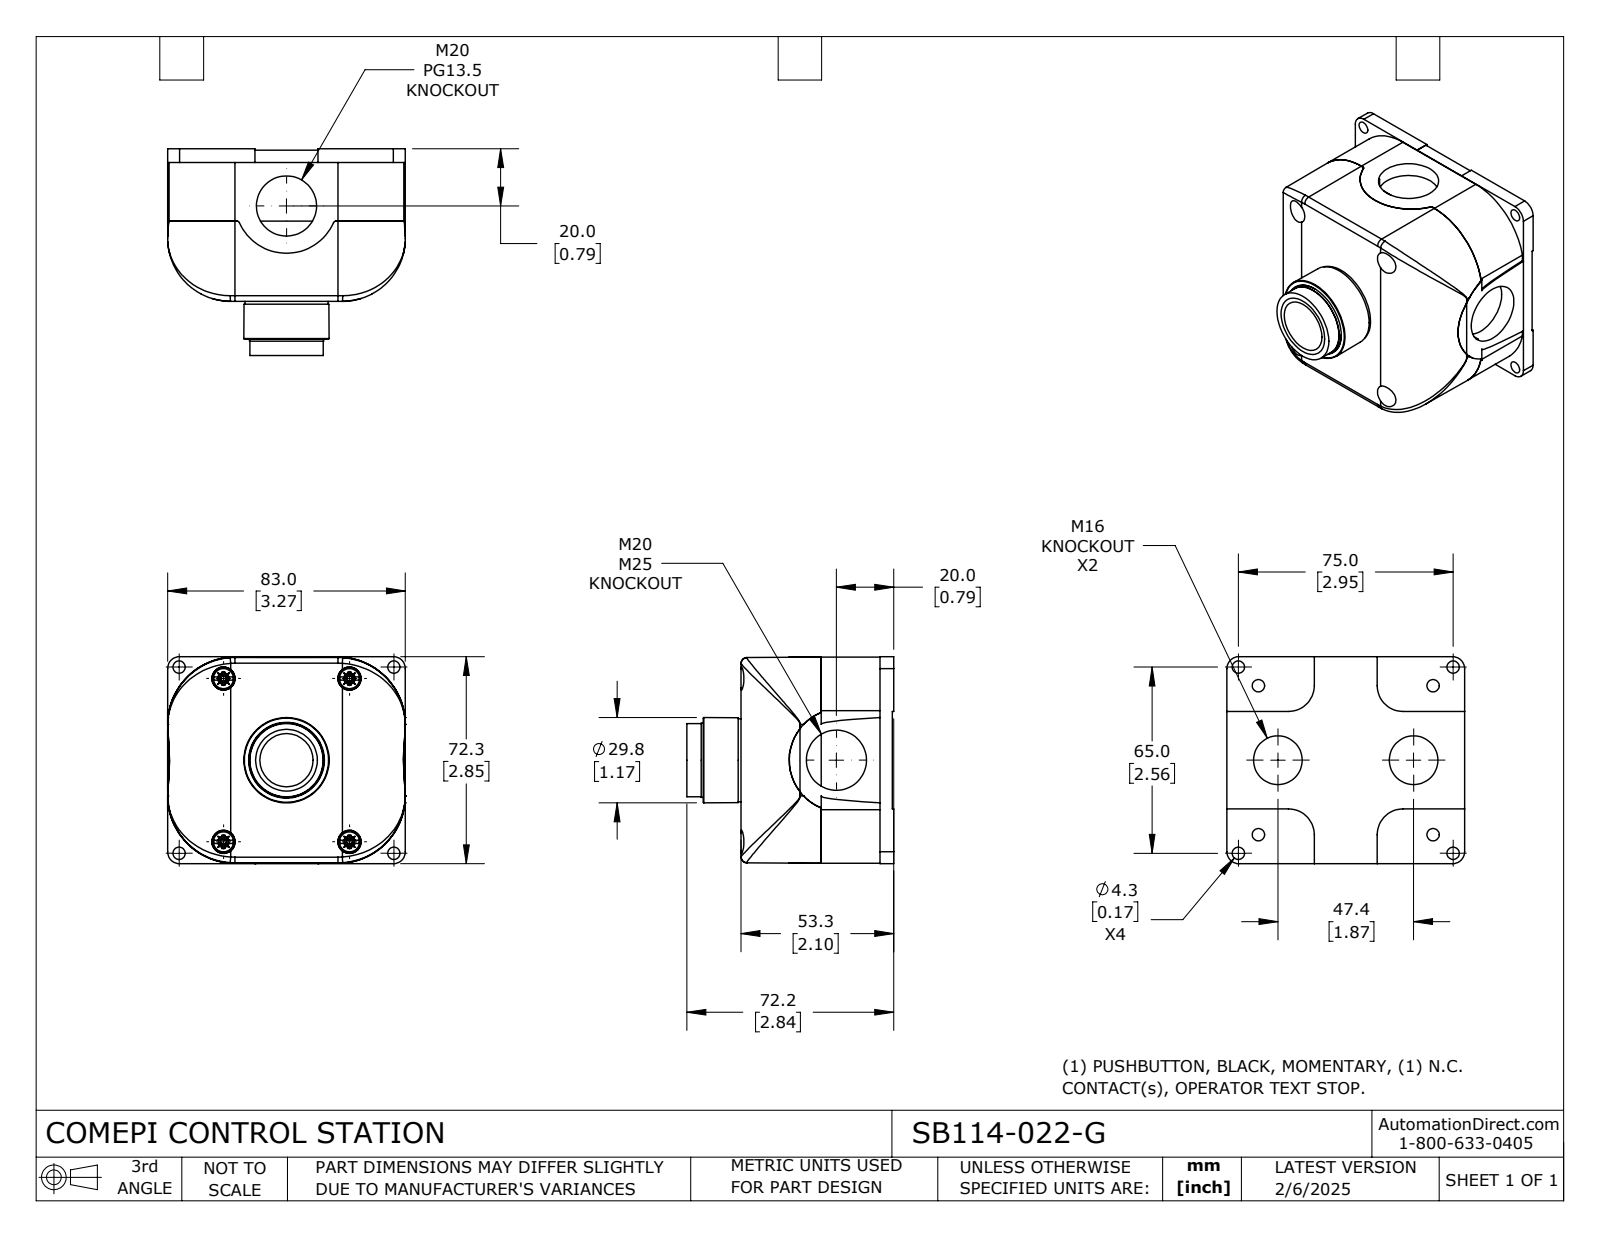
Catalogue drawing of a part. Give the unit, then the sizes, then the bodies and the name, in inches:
Units: inches
Overall size (bounding box): 3.268 × 2.846 × 2.843
Round holes (diameter × count): ⌀0.169 ×8, ⌀0.323 ×4, ⌀0.669 ×2, ⌀0.827 ×2, ⌀0.531 ×1, ⌀0.713 ×1, ⌀0.854 ×1
Round bosses / shafts (diameter × count): ⌀0.276 ×4, ⌀1.142 ×1, ⌀1.02 ×1, ⌀1.008 ×1, ⌀0.748 ×1, ⌀0.728 ×1, ⌀0.63 ×1, ⌀0.614 ×1
Partial cylindrical surfaces — rounded edges, fillets, slot ends (radius × count): R0.035 ×4, R0.079 ×4, R0.354 ×4, R0.38 ×4, R0.925 ×4, R0.008 ×2, R0.01 ×2, R0.709 ×2
Main face-to-face distances: 0.976, 0.098, 0.878, 2.079, 1.98, 1.102, 0.118, 2.098, 0.02, 0.996
Hole centre spacings: 0.376, 1.058, 1.39, 1.578, 1.954, 2.32, 2.367, 2.689
Volume: 12.98 in³ · Surface area: 90.08 in²
Bodies: 4 solids, 551 faces (301 planar, 146 cylindrical, 104 other)
Part name (STEP PRODUCT): SB114-022-G
STEP written by: SolidWorks 2024 (CONFIG_CONTROL_DESIGN)
